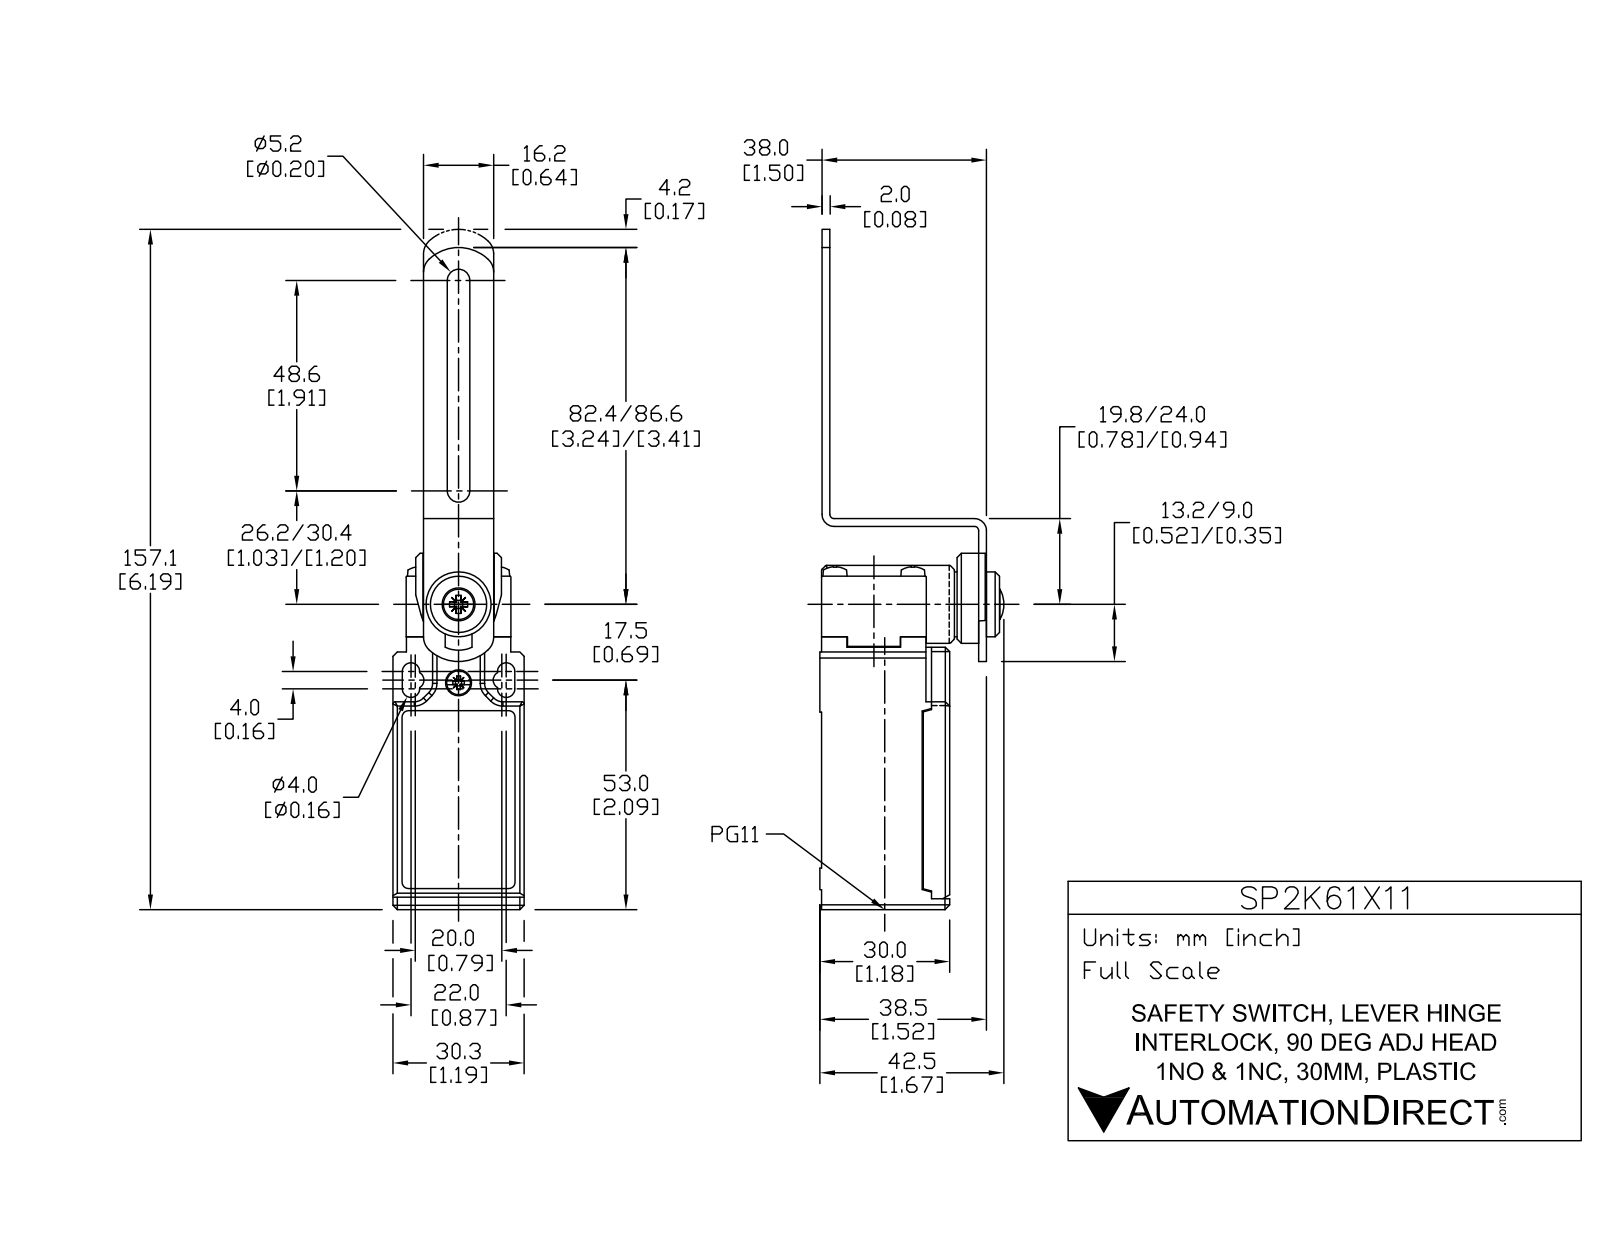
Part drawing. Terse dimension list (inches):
name: SP2K61X11
written by: SolidWorks 2017 (AUTOMOTIVE_DESIGN)
unit: in
bodies: 5 solids, 263 faces (159 planar, 78 cylindrical, 26 other)
size: 6.122 × 1.661 × 1.193
volume: 4.121 in³; area: 30.7 in²
holes: 1× ⌀0.236, 1× ⌀0.299, 1× ⌀0.433, 1× ⌀0.669, 1× ⌀0.748
bosses: 5× ⌀0.22, 1× ⌀0.709, 1× ⌀0.591, 1× ⌀0.276
rounds: 6× R0.079, 4× R0.02, 4× R0.118, 4× R0.157, 3× R0.394, 2× R0.039, 2× R0.102, 2× R0.11
face distances: 0.071, 1.193, 1.165, 1.425, 1.181, 0.124, 1.069, 0.945, 1.102, 0.063
hole spacings: 0.713
